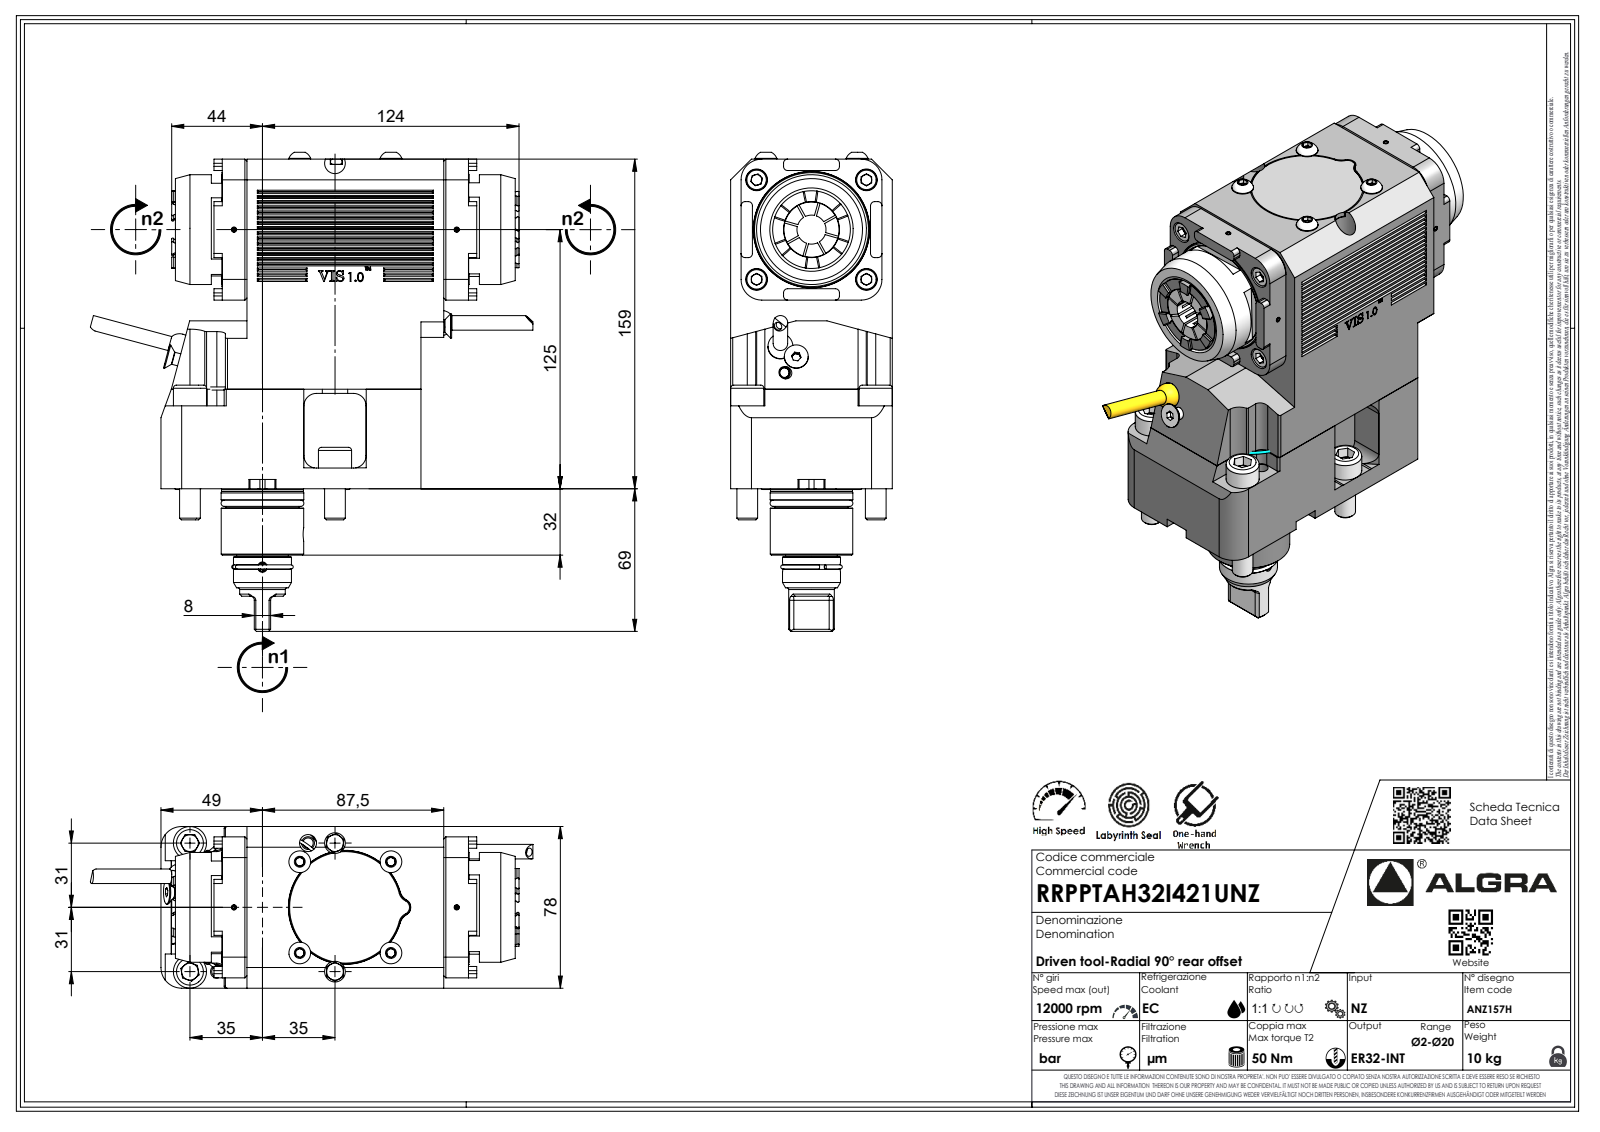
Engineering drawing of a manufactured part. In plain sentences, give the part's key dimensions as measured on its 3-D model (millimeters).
The part is named "RRPPTAH32I421UNZ". Its 3-D file was written by "SolidWorks 2023 (AUTOMOTIVE_DESIGN)". It is 1 solid with 580 faces: 374 planar, 111 cylindrical and 95 other. Overall it measures 227.8 by 213.57 by 78 millimeters. Its volume is 1 580 000 cubic millimeters and its surface area 105 793 square millimeters. Round holes: 1 of diameter 2.1, 1 of diameter 4. Round bosses or shafts: 4 of diameter 10, 2 of diameter 16, 2 of diameter 7, 1 of diameter 53, 1 of diameter 39.9, 1 of diameter 39.8, 1 of diameter 39.5, 1 of diameter 35.1. Partial cylindrical surfaces (rounded edges, fillets, slot ends): 23 of radius 2, 8 of radius 1, 7 of radius 0.33, 7 of radius 0.52, 7 of radius 3.7, 6 of radius 10, 2 of radius 3.5, 2 of radius 4.1. The main face-to-face distances are 78, 159, 34.5, 129.5, 73, 5, 22.6, 141.4, 11.9, 106.9.
